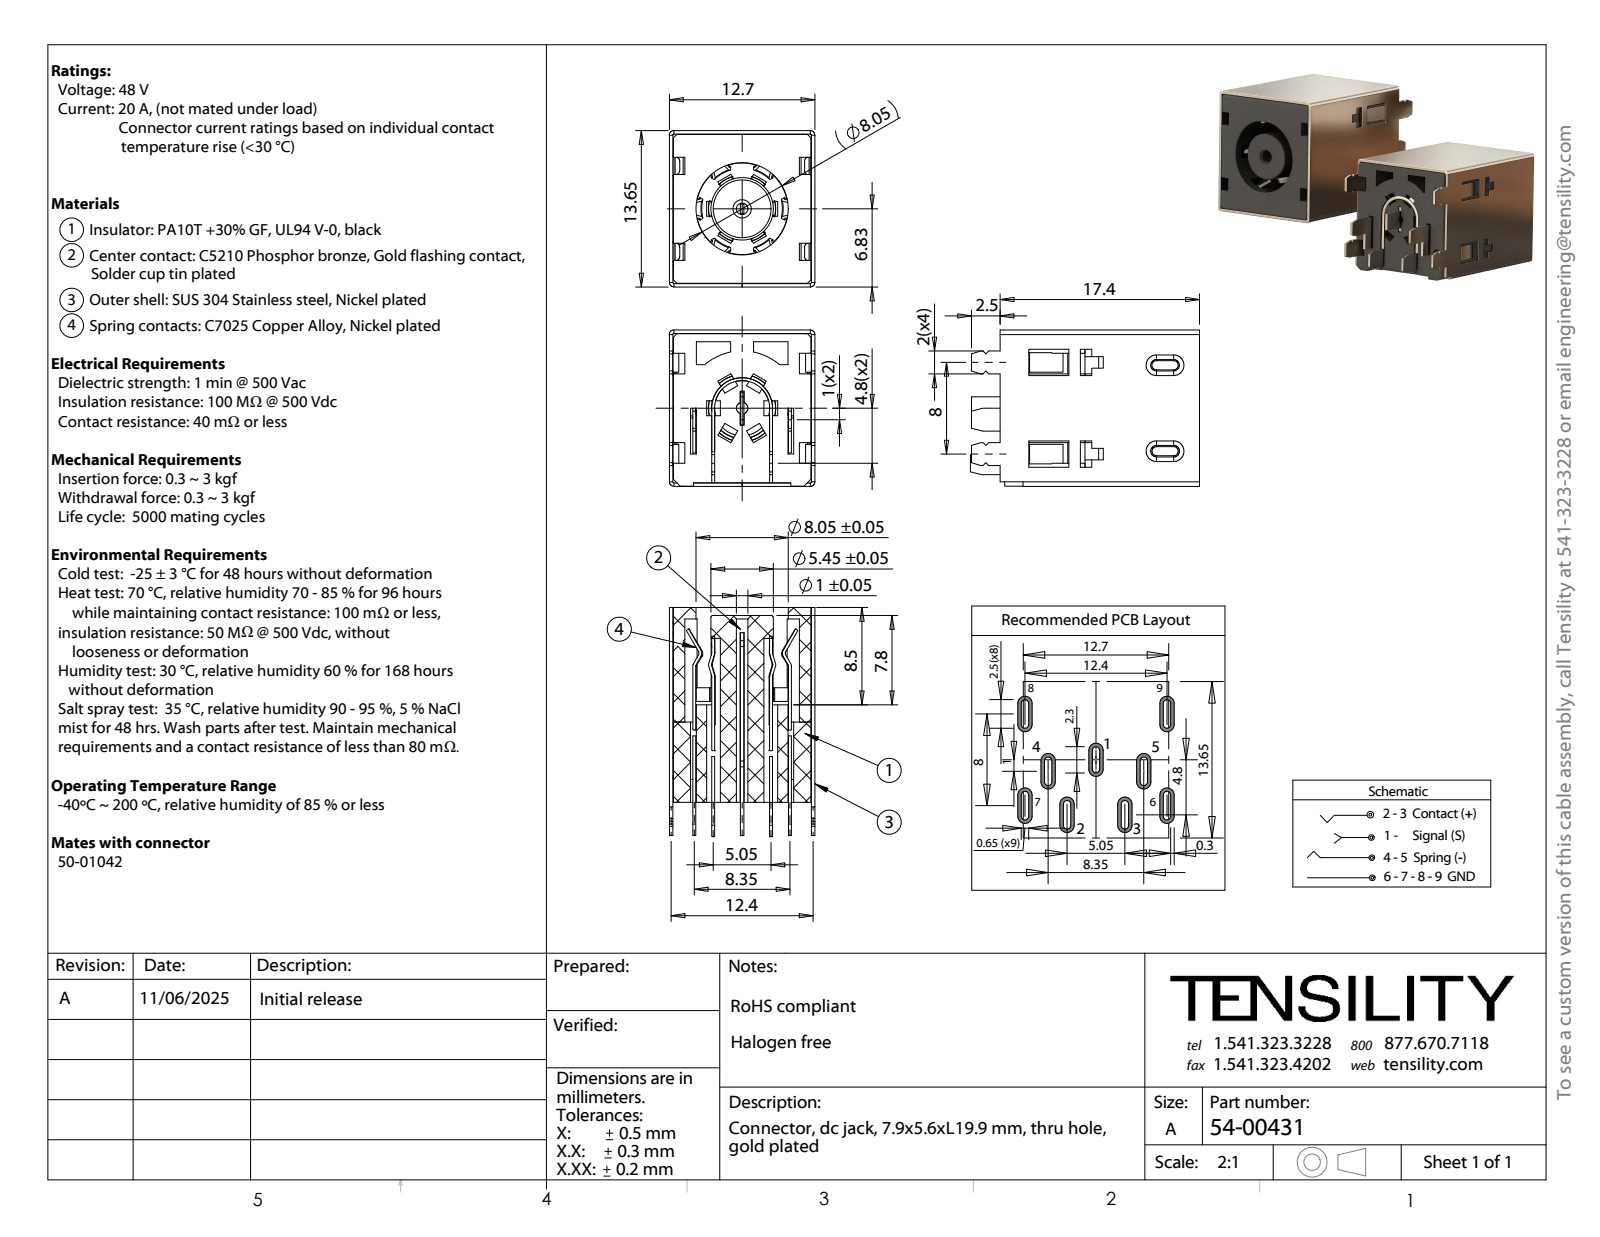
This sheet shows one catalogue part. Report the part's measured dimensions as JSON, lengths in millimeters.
{"part_name": "54-00431-04_默认; 54-00431-02_默认; 54-00431; 54-00431-05_默认 (+3 more)", "step_written_by": "SolidWorks 2025 (CONFIG_CONTROL_DESIGN)", "units": "millimeters", "bodies": {"solids": 6, "faces": 752, "planar": 521, "cylindrical": 78, "other": 153}, "overall_size": [21.1, 13.65, 12.7], "volume_mm3": 2257, "surface_area_mm2": 5779, "round_holes": [[1.6, 2], [1, 1], [4.8, 1], [8, 1], [8.1, 1], [8.6, 1]], "round_bosses_or_shafts": [[5.4, 1], [5.3, 1]], "partial_cylinders_radius": [[0.1, 6], [0.4, 6], [0.25, 2], [0.5, 1], [4.5, 1], [5, 1]], "face_to_face_distances": [12.4, 0.35, 12.35, 12.05, 10, 1.5, 0.32, 9, 13.32, 13.02], "hole_center_spacings": [6.4, 8]}
